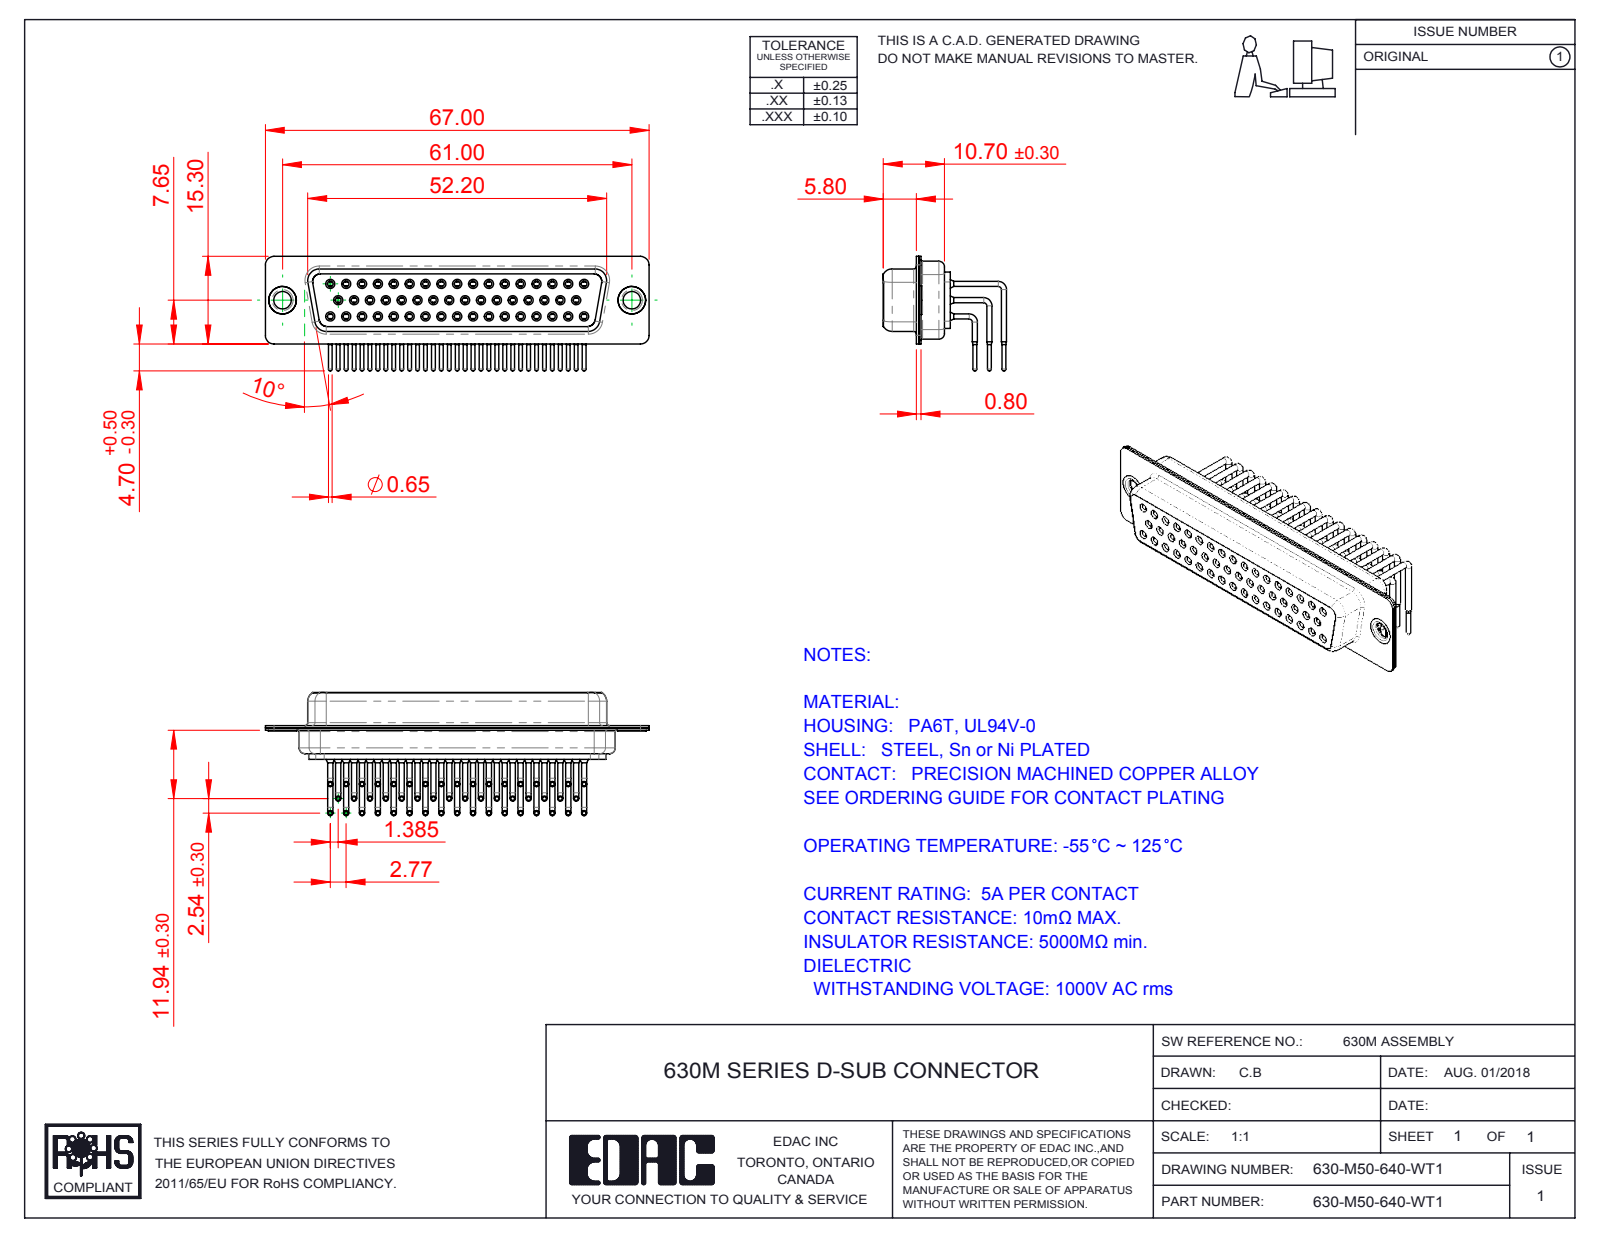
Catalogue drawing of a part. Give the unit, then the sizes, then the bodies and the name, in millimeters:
Units: millimetres
Overall size (bounding box): 67 × 21.53 × 20
Round holes (diameter × count): ⌀1 ×50, ⌀1.1 ×50, ⌀1.7 ×50, ⌀1.8 ×50, ⌀2 ×50, ⌀3.05 ×2, ⌀4 ×2, ⌀4.8 ×2
Round bosses / shafts (diameter × count): ⌀0.9 ×100, ⌀1.6 ×50, ⌀1.5 ×50, ⌀0.65 ×50, ⌀5 ×2, ⌀4.9 ×2, ⌀3.55 ×2
Partial cylindrical surfaces — rounded edges, fillets, slot ends (radius × count): R1.5 ×16, R2 ×12, R1.35 ×8, R1.6 ×8, R0.25 ×4, R0.5 ×4, R0.6 ×4, R0.65 ×4
Main face-to-face distances: 0.4, 1.35, 11.85, 0.85, 2.2, 5.5, 12.25, 5.9, 10.5, 10.05
Hole centre spacings: 2.77, 3.16, 5.54, 8.31, 11.08, 13.85, 16.62, 19.39
Volume: 6 941 mm³ · Surface area: 16 414 mm²
Bodies: 55 solids, 2903 faces (817 planar, 1271 cylindrical, 815 other)
Part name (STEP PRODUCT): 630M Shell Front_50 Contacts; 630M Contact Row 1_50 Contacts; 630M Contact Row 2_50 Contacts; 630-M50-640-WT1 (+4 more)
STEP written by: SolidWorks 2016 (CONFIG_CONTROL_DESIGN)
